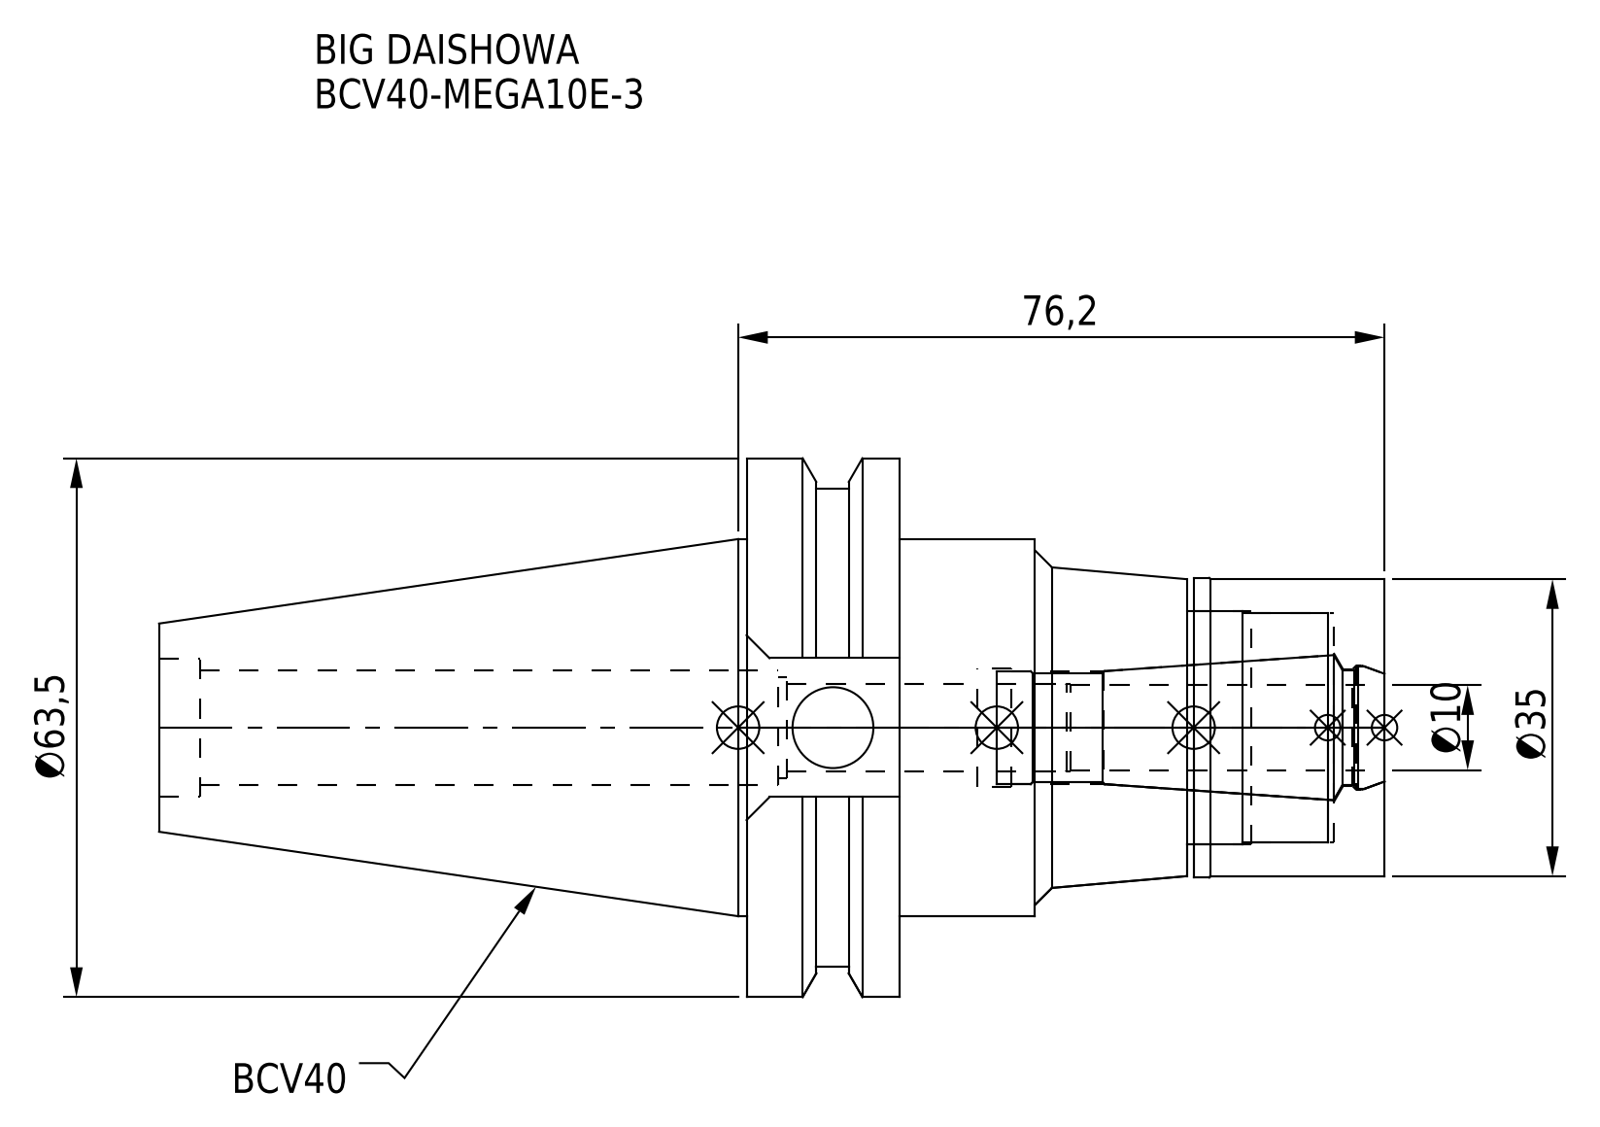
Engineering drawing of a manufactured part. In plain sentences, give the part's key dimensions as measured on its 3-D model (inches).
The part is named "BCV40-MEGA10E-3; BCV40-MEGA10E-3-100-FreeParts; DXF_TEMP_ASSY_ASM_4_ASM.stp; BCV40ME10030-010_ASM.stp (+3 more)". Its 3-D file was written by "SolidWorks 2019 (CONFIG_CONTROL_DESIGN)". It is 2 solids with 93 faces: 31 planar, 42 cylindrical and 20 other. Overall it measures 5.687 by 2.5 by 2.415 inches. Its volume is 9.857 cubic inches and its surface area 52.36 square inches. Round holes: 1 of diameter 0.375, 1 of diameter 0.409, 1 of diameter 0.472, 1 of diameter 0.524, 1 of diameter 0.535, 1 of diameter 0.543, 1 of diameter 0.547, 1 of diameter 0.579, 1 of diameter 0.643, 1 of diameter 1.063, 1 of diameter 1.083. Round bosses or shafts: 1 of diameter 2.5, 1 of diameter 2.219, 1 of diameter 1.75, 1 of diameter 1.39, 1 of diameter 1.378. The main face-to-face distances are 0.711, 2.25, 2.961, 0.236, 0.886, 1.364, 2.075, 0.917, 0.031, 1.333.
